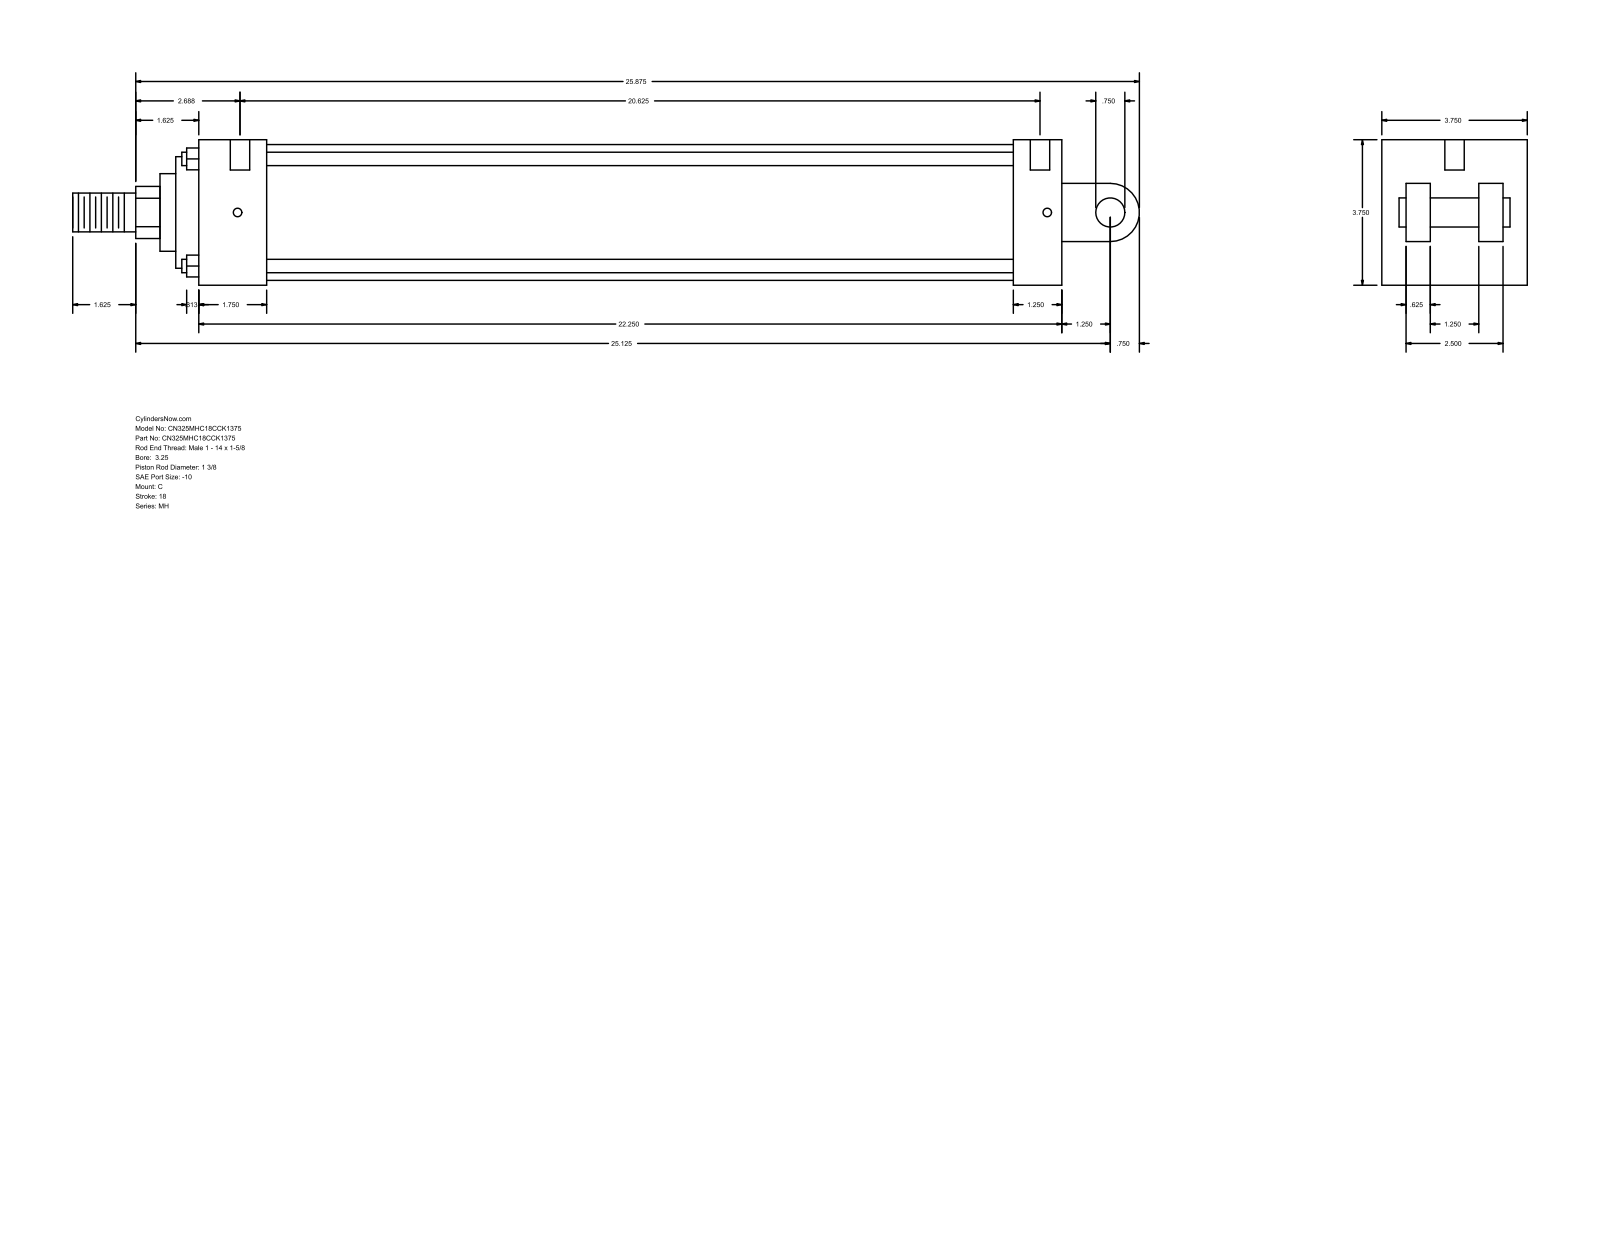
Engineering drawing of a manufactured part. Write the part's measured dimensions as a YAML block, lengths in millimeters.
part_name: "MH_C__0325_1.375"
step_written_by: "GSSL Pune (CONFIG_CONTROL_DESIGN)"
units: millimeters
bodies: {solids: 0, faces: 101, planar: 71, cylindrical: 30, other: 0}
overall_size: [698.5, 95.25, 95.25]
round_holes:
  - {diameter: 5.56, count: 4}
  - {diameter: 12.7, count: 2}
round_bosses_or_shafts:
  - {diameter: 8.76, count: 4}
  - {diameter: 88.9, count: 1}
  - {diameter: 73.03, count: 1}
  - {diameter: 50.8, count: 1}
  - {diameter: 34.92, count: 1}
  - {diameter: 25.4, count: 1}
  - {diameter: 19.05, count: 1}
partial_cylinders:
  - {radius: 17.06, count: 1}
  - {radius: 19.05, count: 1}
face_to_face_distances: [95.24, 15.87, 63.5, 565.15, 31.74, 79.37, 47.63, 44.45, 533.4, 488.95]
hole_center_spacings: [530.23, 1.59, 4.76, 523.88, 525.47, 528.64]
